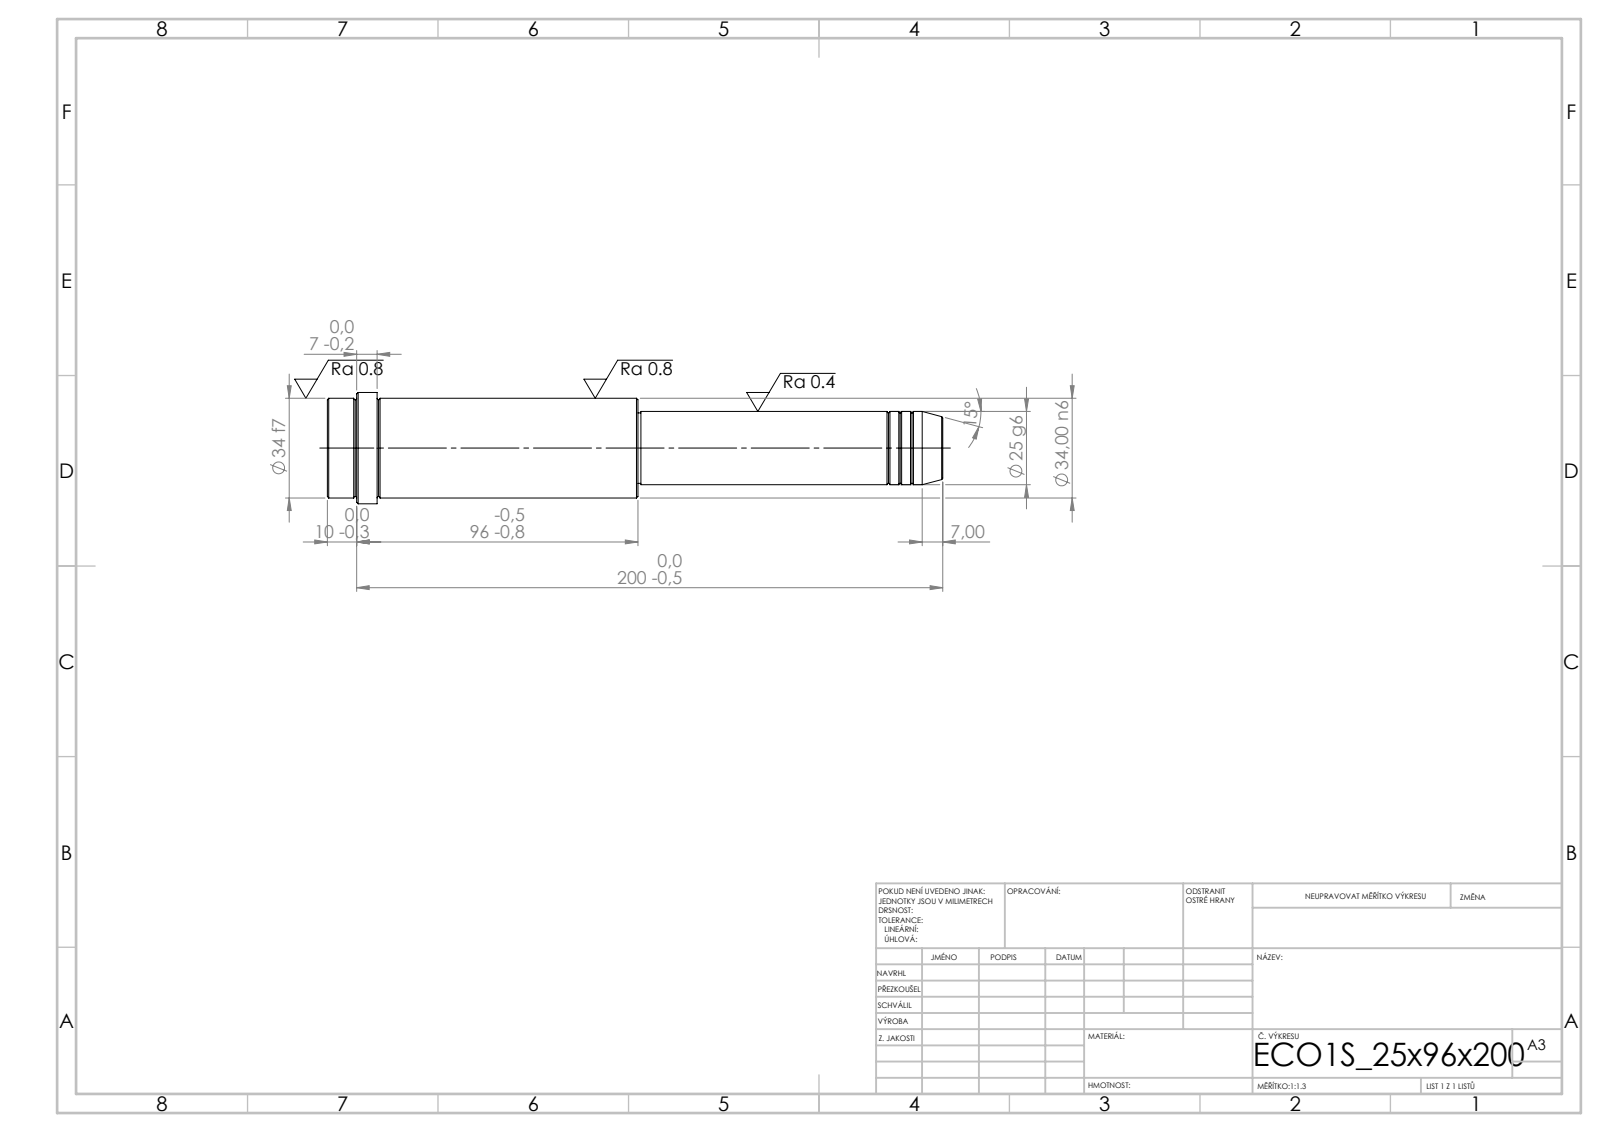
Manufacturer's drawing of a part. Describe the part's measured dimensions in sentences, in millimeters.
Its 3-D file was written by "SolidWorks 2019 (CONFIG_CONTROL_DESIGN)". It is 1 solid with 52 faces: 6 planar, 16 cylindrical and 30 other. Overall it measures 210 by 38 by 38 millimeters. Its volume is 148 129 cubic millimeters and its surface area 21 896 square millimeters. Round bosses or shafts: 1 of diameter 38, 1 of diameter 34, 1 of diameter 25, 1 of diameter 24. The main face-to-face distances are 106, 104, 210, 193, 89, 17, 200, 96, 7, 10.
